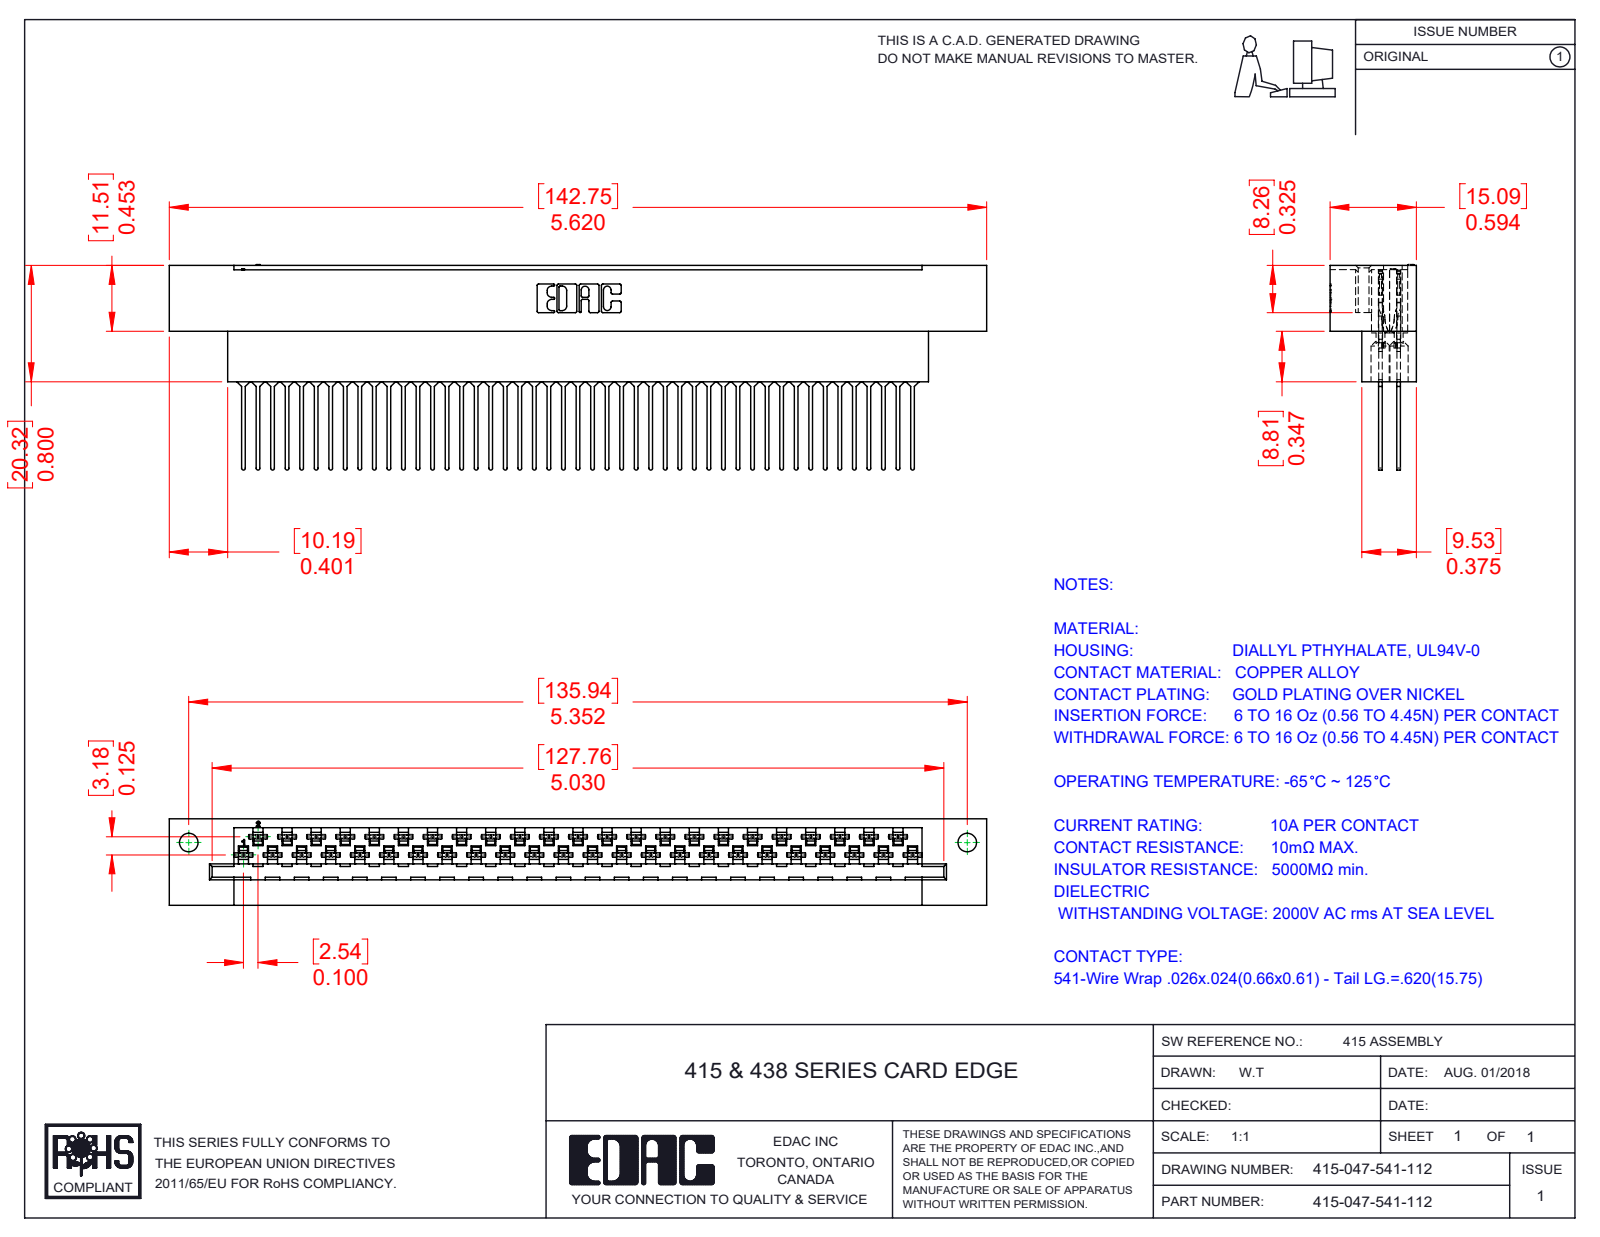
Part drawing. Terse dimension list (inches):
name: 415-210-001_415-210-047-112; 516-290-001_541; 415-047-541-112
written by: SolidWorks 2016 (CONFIG_CONTROL_DESIGN)
unit: in
bodies: 48 solids, 4750 faces (3039 planar, 1266 cylindrical, 445 other)
size: 5.62 × 1.411 × 0.594
volume: 1.629 in³; area: 48.37 in²
holes: 47× ⌀0.05, 47× ⌀0.13, 2× ⌀0.128
rounds: 188× R0.012, 188× R0.022, 94× R0.007, 94× R0.008, 94× R0.016, 94× R0.08, 47× R0.013, 22× R0.01
face distances: 0.125, 0.024, 0.074, 0.05, 0.594, 0.076, 0.026, 0.26, 0.334, 0.236
hole spacings: 0.2, 0.4, 0.6, 0.8, 1, 1.2, 1.4, 0.1
